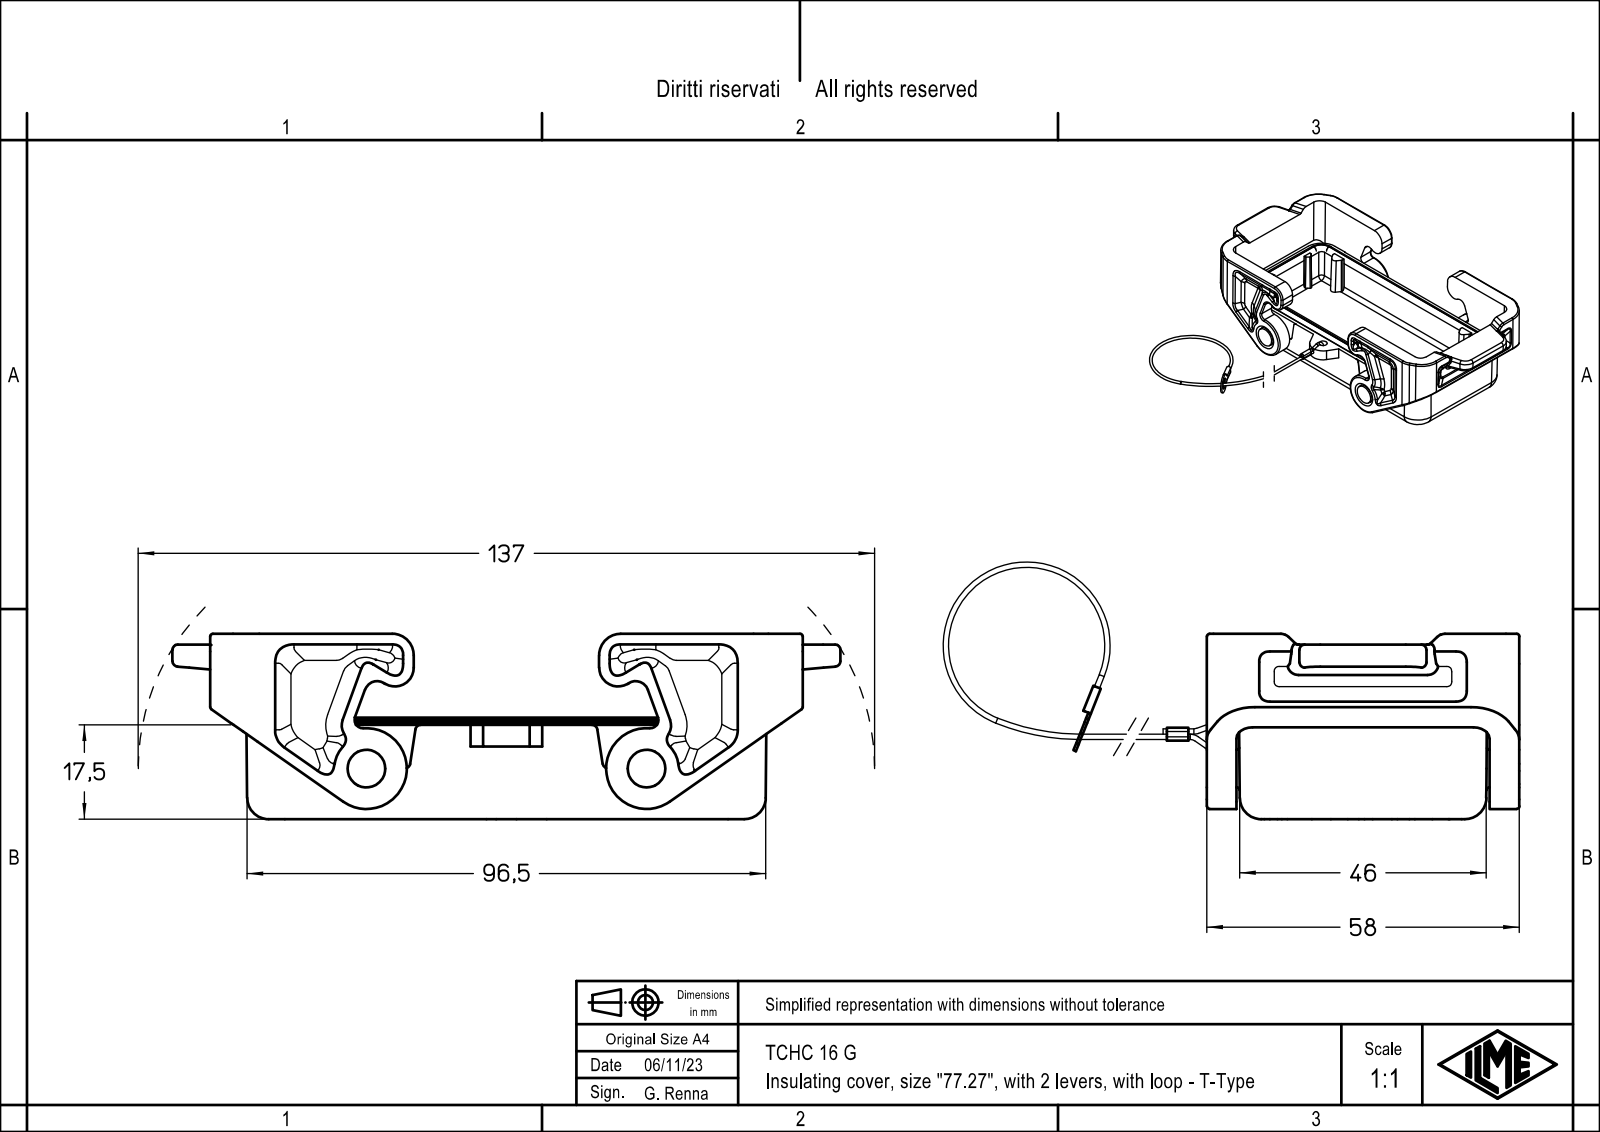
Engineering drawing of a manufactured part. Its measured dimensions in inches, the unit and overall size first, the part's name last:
Units: inches
Overall size (bounding box): 8.971 × 4.882 × 1.36
Round holes (diameter × count): ⌀0.118 ×1, ⌀0.165 ×1
Round bosses / shafts (diameter × count): ⌀0.039 ×5, ⌀0.276 ×3
Partial cylindrical surfaces — rounded edges, fillets, slot ends (radius × count): R0.006 ×44, R0.039 ×40, R0.059 ×18, R0.051 ×16, R0.118 ×16, R0.02 ×12, R0.079 ×12, R0.157 ×10
Main face-to-face distances: 0.217, 2.067, 1.85, 1.354, 1.138, 0.472, 2.283, 0.689, 0.665, 3.937
Volume: 4.035 in³ · Surface area: 54.57 in²
Bodies: 1 solid, 604 faces (214 planar, 302 cylindrical, 88 other)
Part name (STEP PRODUCT): TCHC 16 G
STEP written by: Creo Elements/Direct Modeling 20.1B 02-Apr-2019 (C) Parametric Technology GmbH (AUTOMOTIVE_DESIGN)
